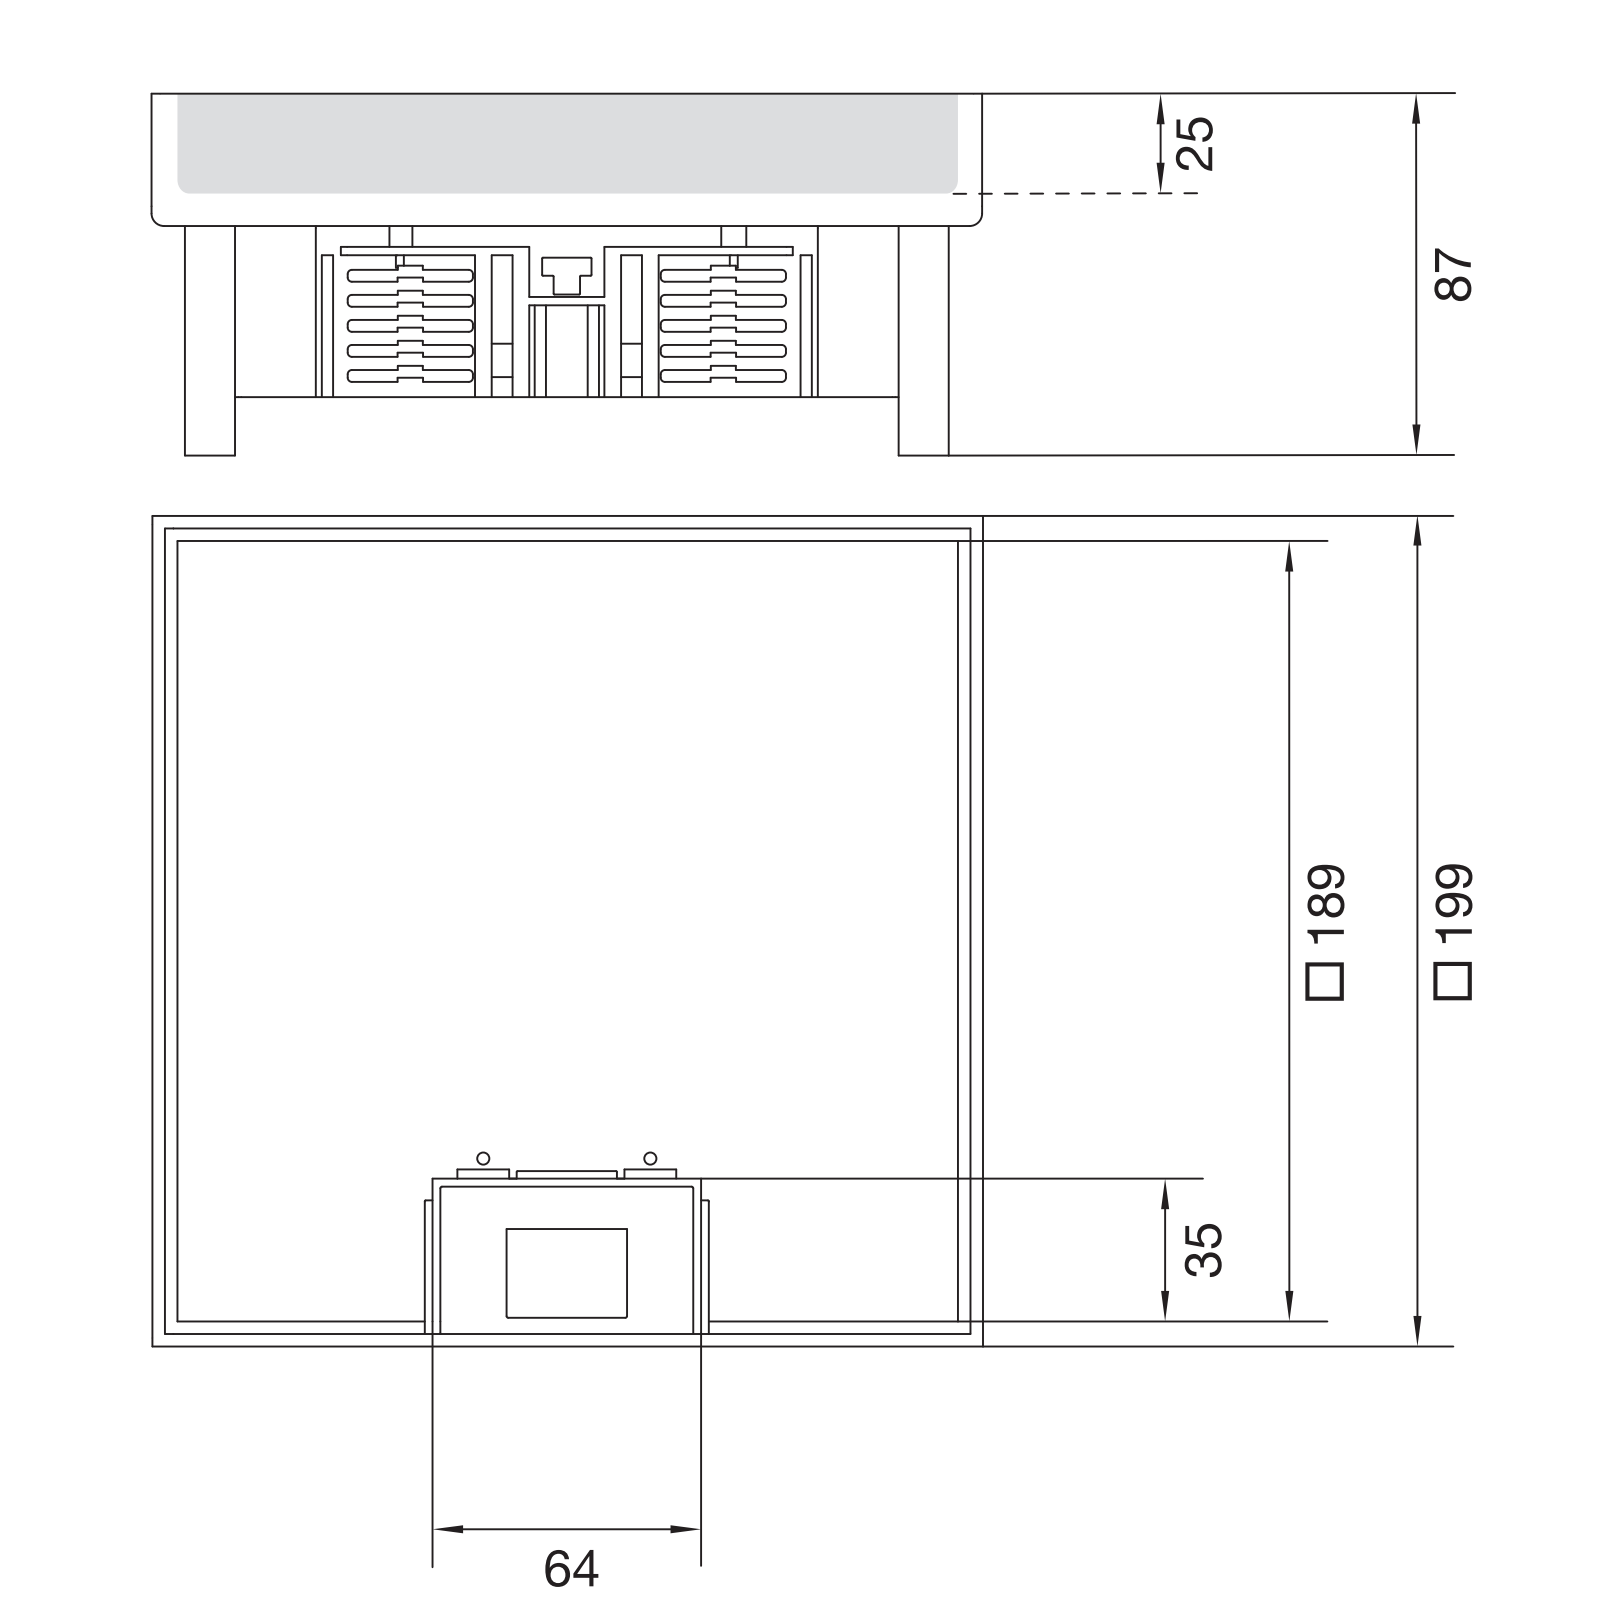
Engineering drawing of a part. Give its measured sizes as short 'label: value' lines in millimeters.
name: T-00597_1_1; T-00595_1_1; T-00806_ASM_1_1_ASM; U09001_1_1 (+8 more)
written by: CREO PARAMETRIC BY PTC INC, 2022281 (AUTOMOTIVE_DESIGN)
unit: mm
bodies: 10 solids, 306 faces (229 planar, 67 cylindrical, 10 other)
size: 199 × 199 × 87
volume: 268 077 mm³; area: 267 678 mm²
holes: 4× ⌀6.8, 4× ⌀8.5, 2× ⌀2.7
bosses: 4× ⌀12, 4× ⌀9.85
rounds: 8× R1, 8× R3, 5× R105, 1× R6.6, 1× R107
face distances: 2, 3, 5, 194, 197, 2.5, 174.5, 1, 196, 192
hole spacings: 171, 72.47, 109.96, 154.56, 175.3, 241.83, 40
